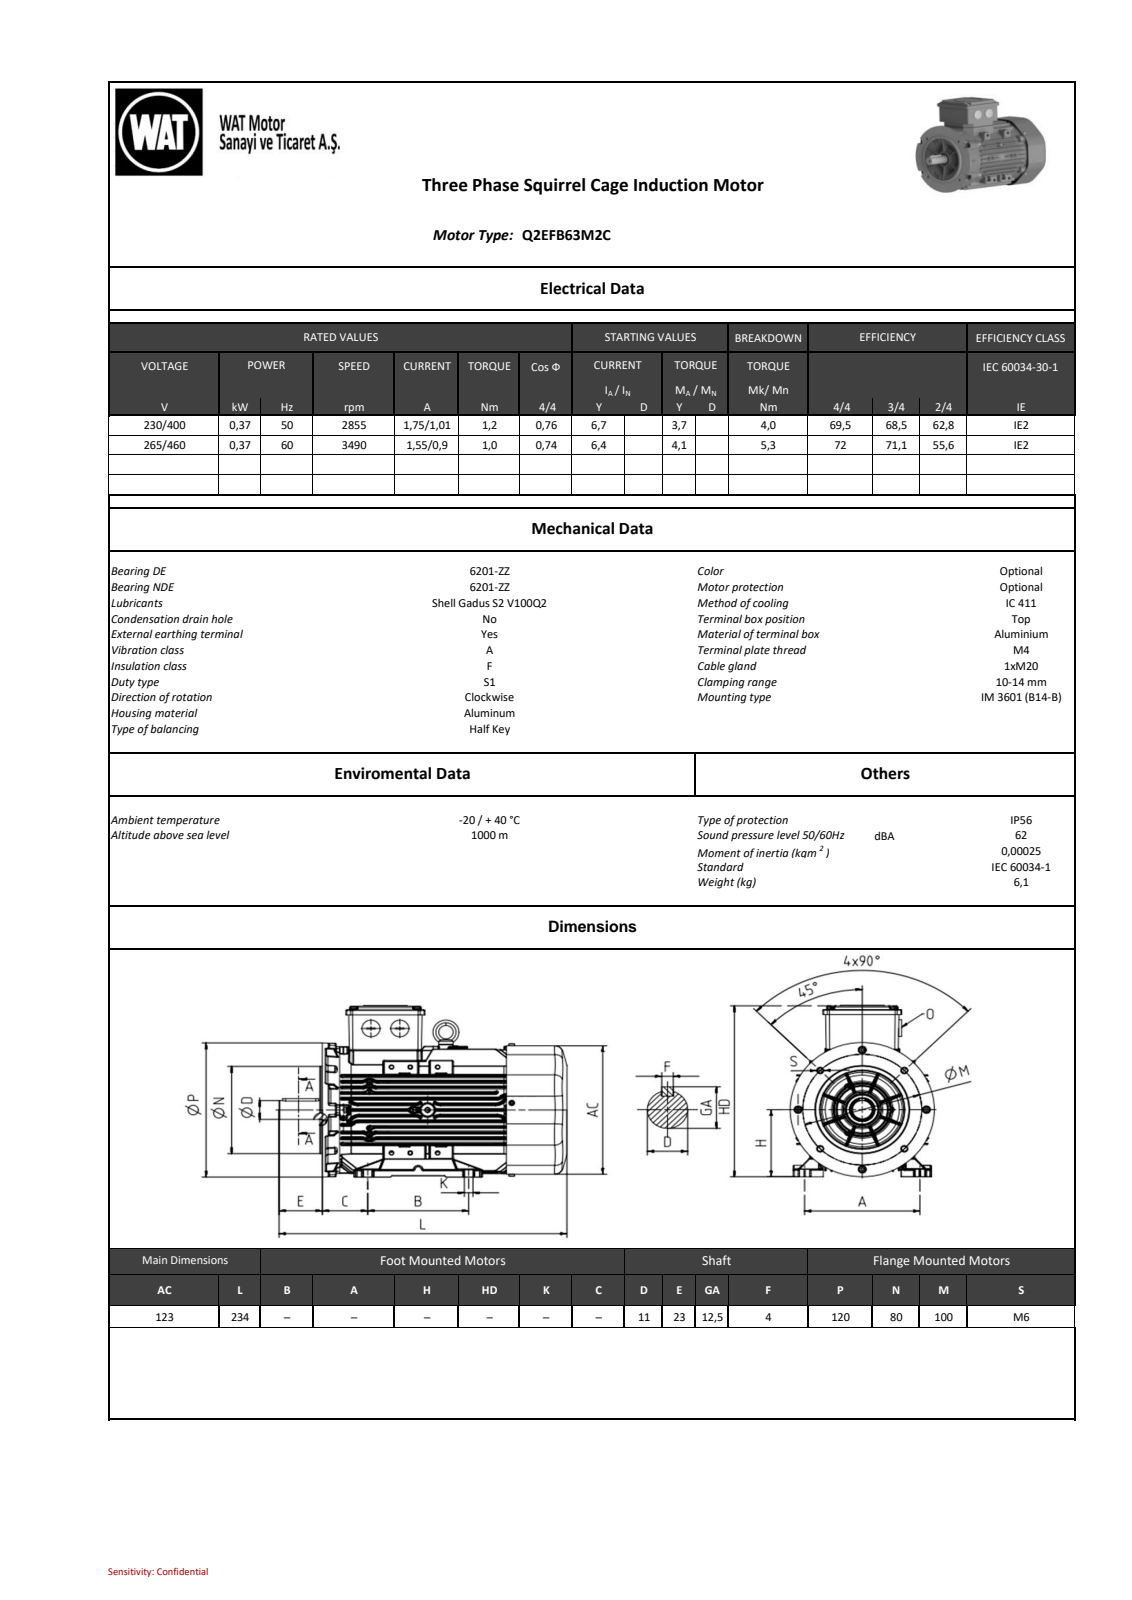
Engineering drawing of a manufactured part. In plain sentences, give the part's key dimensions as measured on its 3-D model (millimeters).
The part is named "QE Series_ 63_B14b_Deep Cover__stp_objects". Its 3-D file was written by "SIEMENS PLM Software NX2206.8101 (AP203_CONFIGURATION_CONTROLLED_3D_DESIGN_OF_MECHANICAL_PARTS_AND_ASSEMBLIES_MIM_LF)". It is 0 solids with 1368 faces: 785 planar, 381 cylindrical and 202 other. Overall it measures 233.47 by 160.6 by 126.28 millimeters. Round holes: 8 of diameter 3.65, 4 of diameter 2.5, 4 of diameter 6, 3 of diameter 3, 1 of diameter 5, 1 of diameter 8, 1 of diameter 14.96, 1 of diameter 19, 1 of diameter 19.84, 1 of diameter 57, 1 of diameter 72, 1 of diameter 121. Round bosses or shafts: 8 of diameter 8, 4 of diameter 4.8, 4 of diameter 4, 1 of diameter 123, 1 of diameter 120, 1 of diameter 80, 1 of diameter 61, 1 of diameter 25.28. Partial cylindrical surfaces (rounded edges, fillets, slot ends): 101 of radius 0.5, 56 of radius 1, 33 of radius 2, 16 of radius 1.5, 8 of radius 4, 7 of radius 8, 6 of radius 0.3, 5 of radius 0.1. The main face-to-face distances are 7.02, 27.96, 28.05, 6.93, 13.81, 6.88, 181.5, 5, 21.03, 14.16. The hole center spacings are 54, 63, 70.71, 82.98, 10, 50, 5, 31.5.
